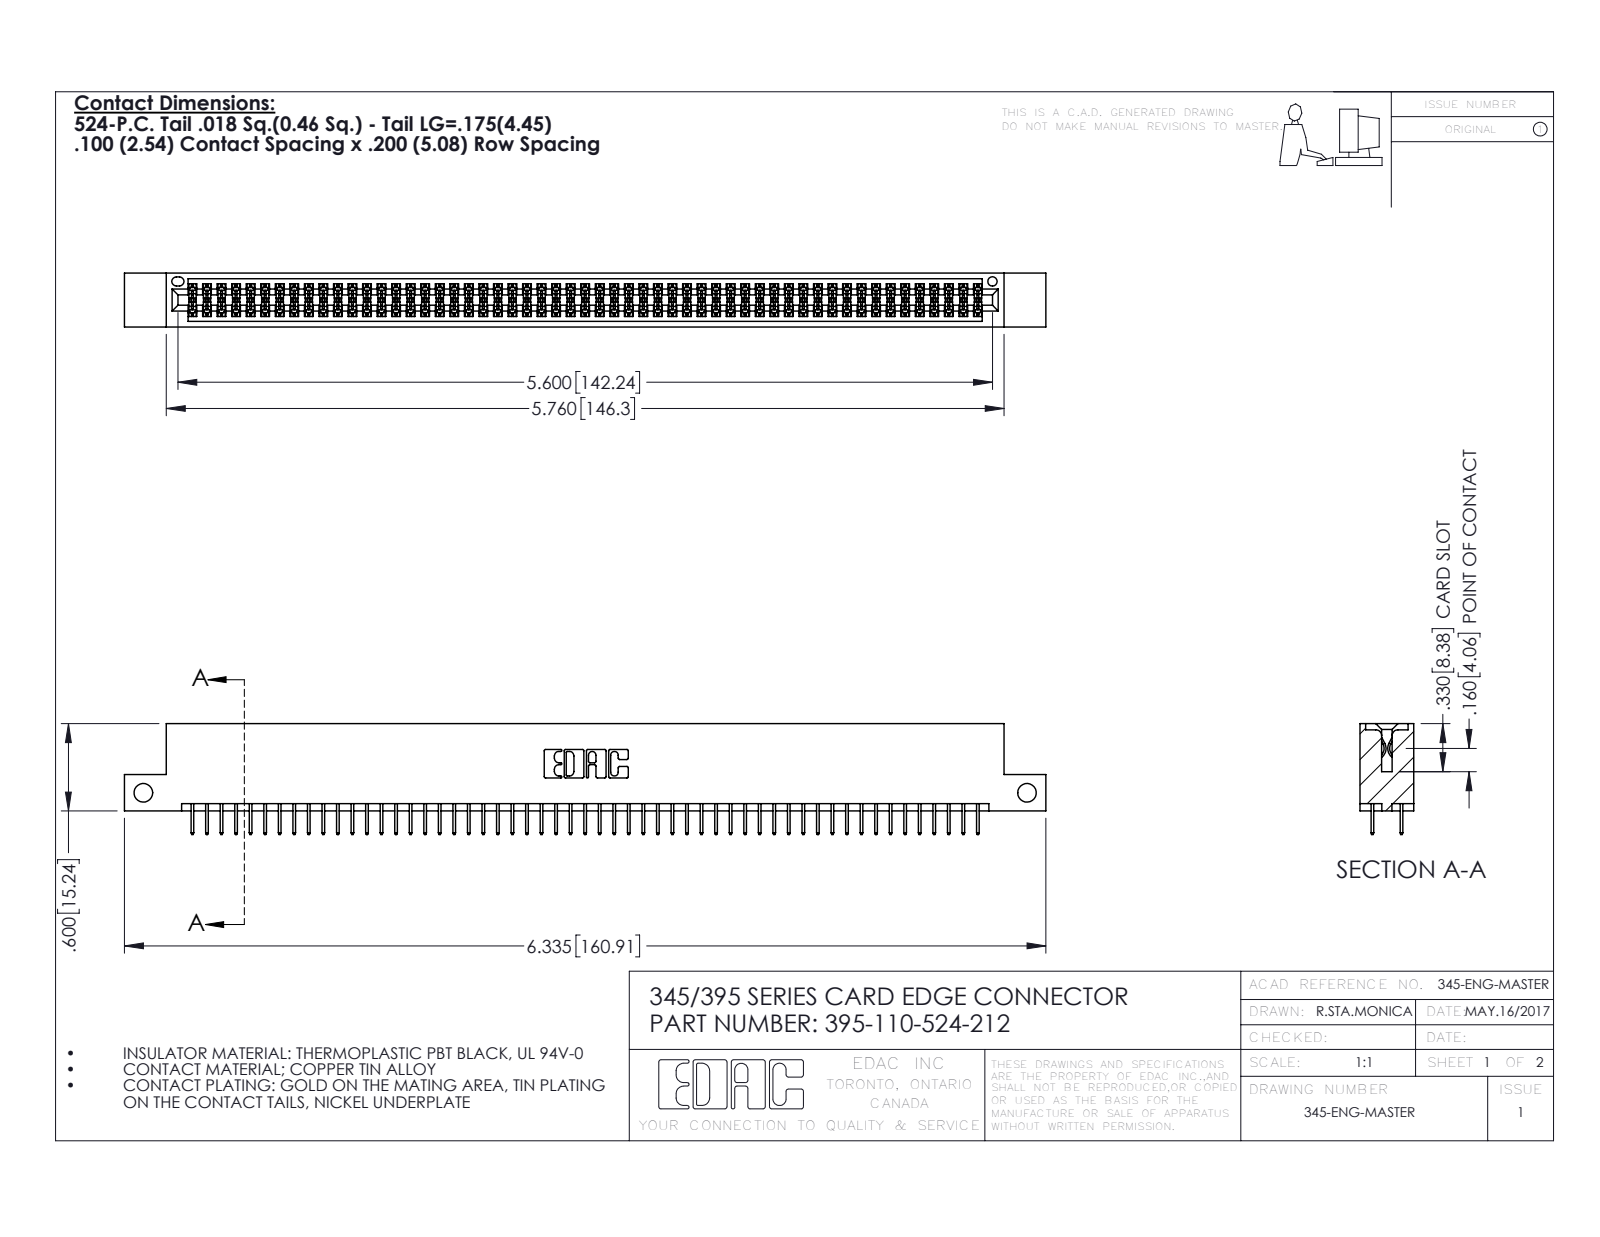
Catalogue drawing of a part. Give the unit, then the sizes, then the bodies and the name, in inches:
Units: inches
Overall size (bounding box): 6.335 × 0.762 × 0.37
Round holes (diameter × count): ⌀0.128 ×2, ⌀0.064 ×1
Partial cylindrical surfaces — rounded edges, fillets, slot ends (radius × count): R0.006 ×165, R0.01 ×22, R0.007 ×6, R0.031 ×6, R0.026 ×3, R0.014 ×2, R0.019 ×2, R0.022 ×2
Main face-to-face distances: 0.298, 0.072, 0.2, 0.37, 0.098, 0.272, 0.025, 0.225, 0.072, 0.175
Hole centre spacings: 6.075
Volume: 0.946 in³ · Surface area: 35.01 in²
Bodies: 111 solids, 6066 faces (4370 planar, 1696 cylindrical, 0 other)
Part name (STEP PRODUCT): 345 Part_Flush Mounting Lugs - Side Mount; 395-110-524-212; 345-292-001_345-293-124
STEP written by: SolidWorks 2016 (CONFIG_CONTROL_DESIGN)
